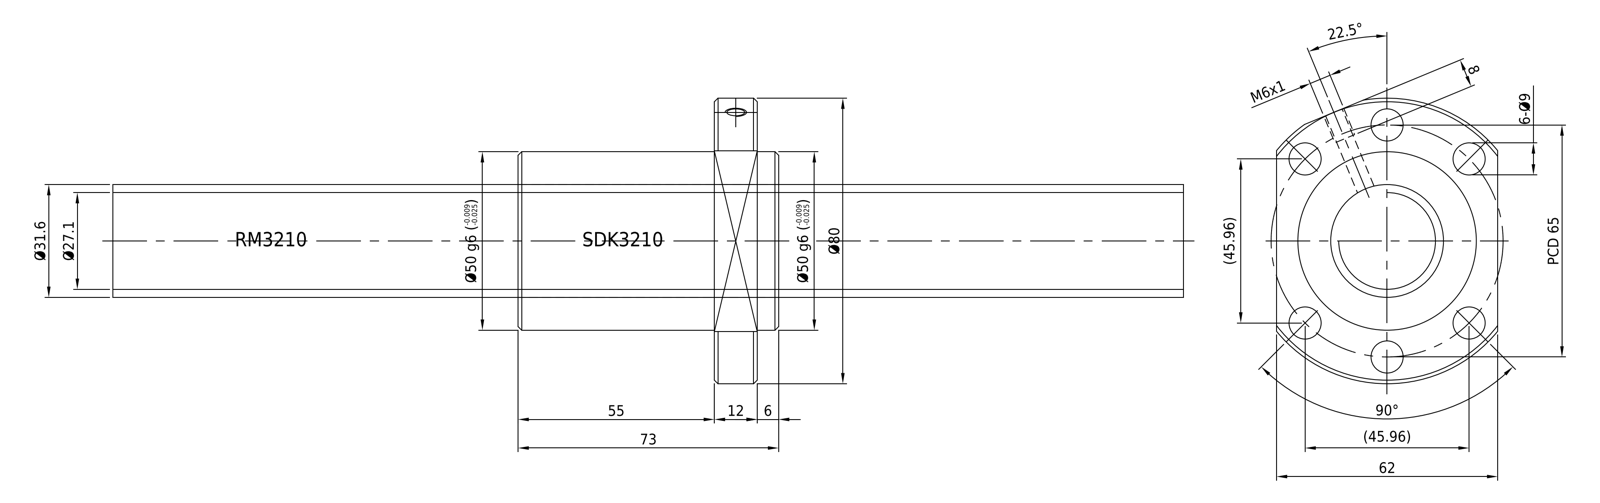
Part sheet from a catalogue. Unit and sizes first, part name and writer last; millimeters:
Units: millimetres
Overall size (bounding box): 300 × 80 × 62
Round holes (diameter × count): ⌀9 ×6, ⌀3 ×1, ⌀5 ×1, ⌀32 ×1
Round bosses / shafts (diameter × count): ⌀50 ×1, ⌀31.6 ×1
Partial cylindrical surfaces — rounded edges, fillets, slot ends (radius × count): R40 ×1
Main face-to-face distances: 12, 113.5, 186.5, 67, 55, 6, 18, 73, 119.5, 131.5
Hole centre spacings: 32.5, 24.87, 45.96, 60.05, 65
Volume: 344 087 mm³ · Surface area: 59 761 mm²
Bodies: 2 solids, 48 faces (9 planar, 27 cylindrical, 12 other)
Part name (STEP PRODUCT): RM3210; SDK3210
STEP written by: SolidWorks 2013 (CONFIG_CONTROL_DESIGN)
